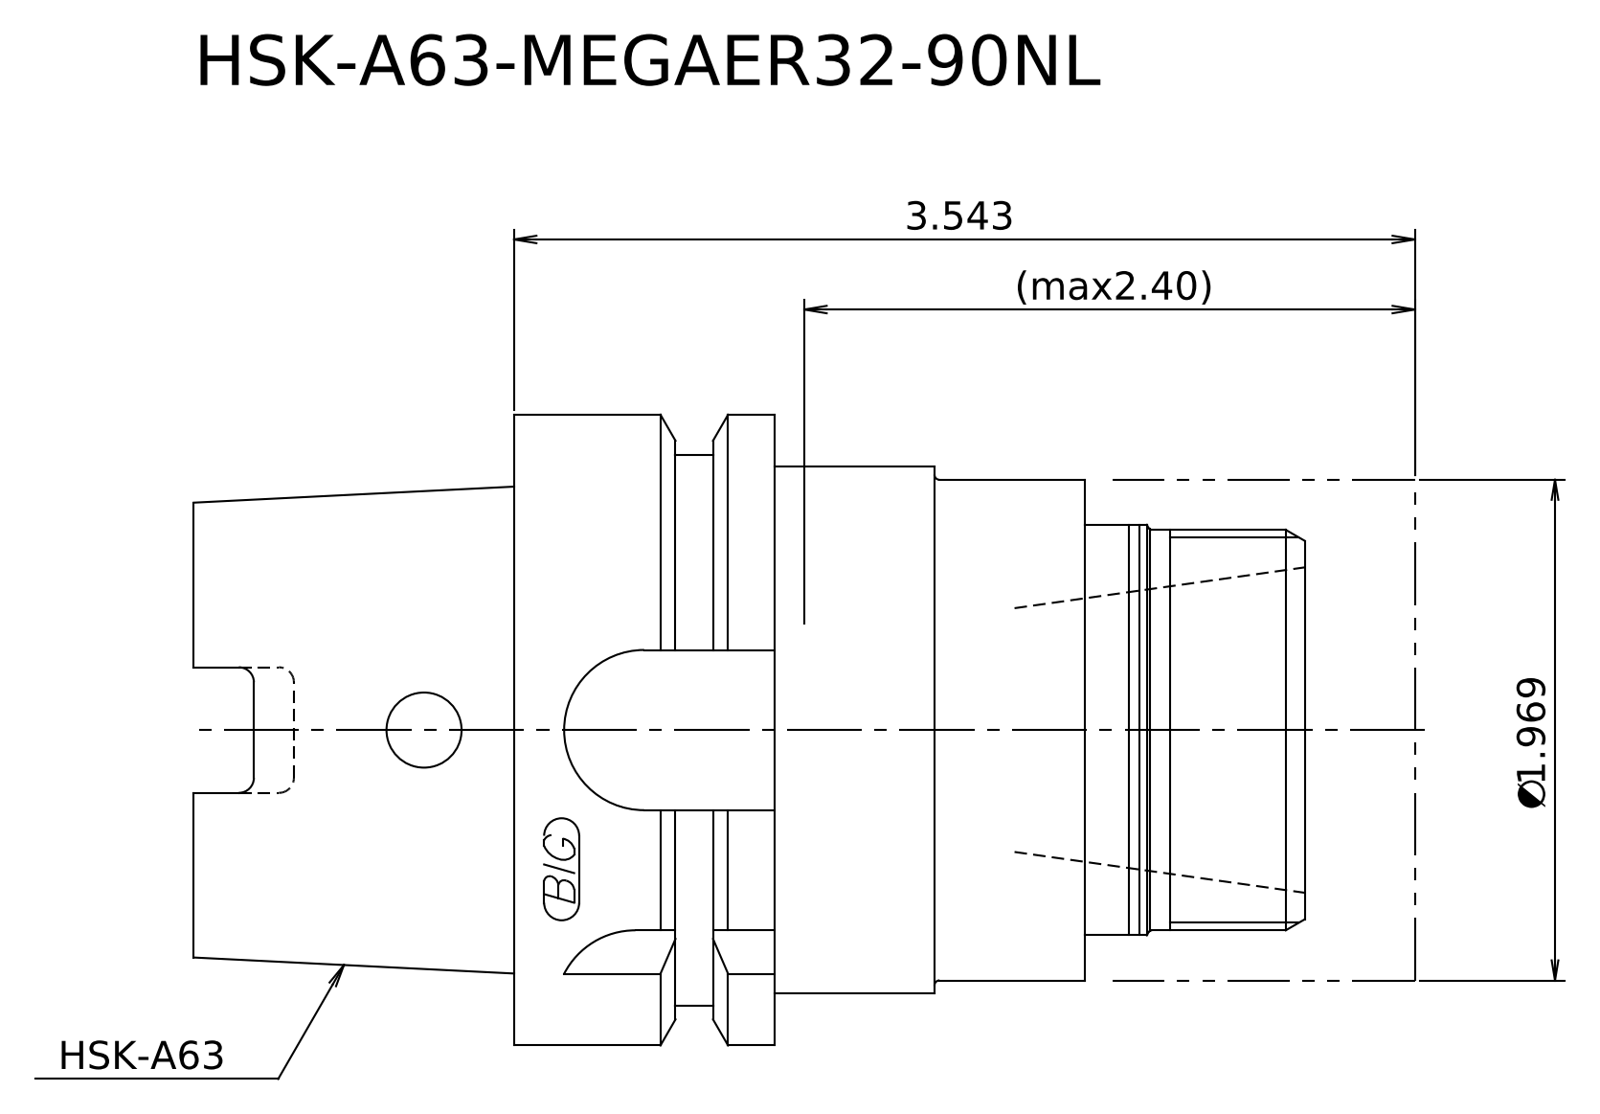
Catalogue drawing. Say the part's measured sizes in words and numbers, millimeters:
Its 3-D file was written by "Kubotek KeyCreator 2011 V10.0.2 (22737) (automotive_design)". It is 2 solids with 24 faces: 10 planar, 8 cylindrical and 6 other. Overall it measures 122 by 63 by 63 millimeters. Its volume is 284 585 cubic millimeters and its surface area 33 102 square millimeters. Round bosses or shafts: 1 of diameter 63, 1 of diameter 55, 1 of diameter 52.6, 1 of diameter 50, 1 of diameter 41, 1 of diameter 40. The main face-to-face distances are 30.2, 122, 91.8, 90, 59.8, 32, 11, 19.2, 79, 111.
